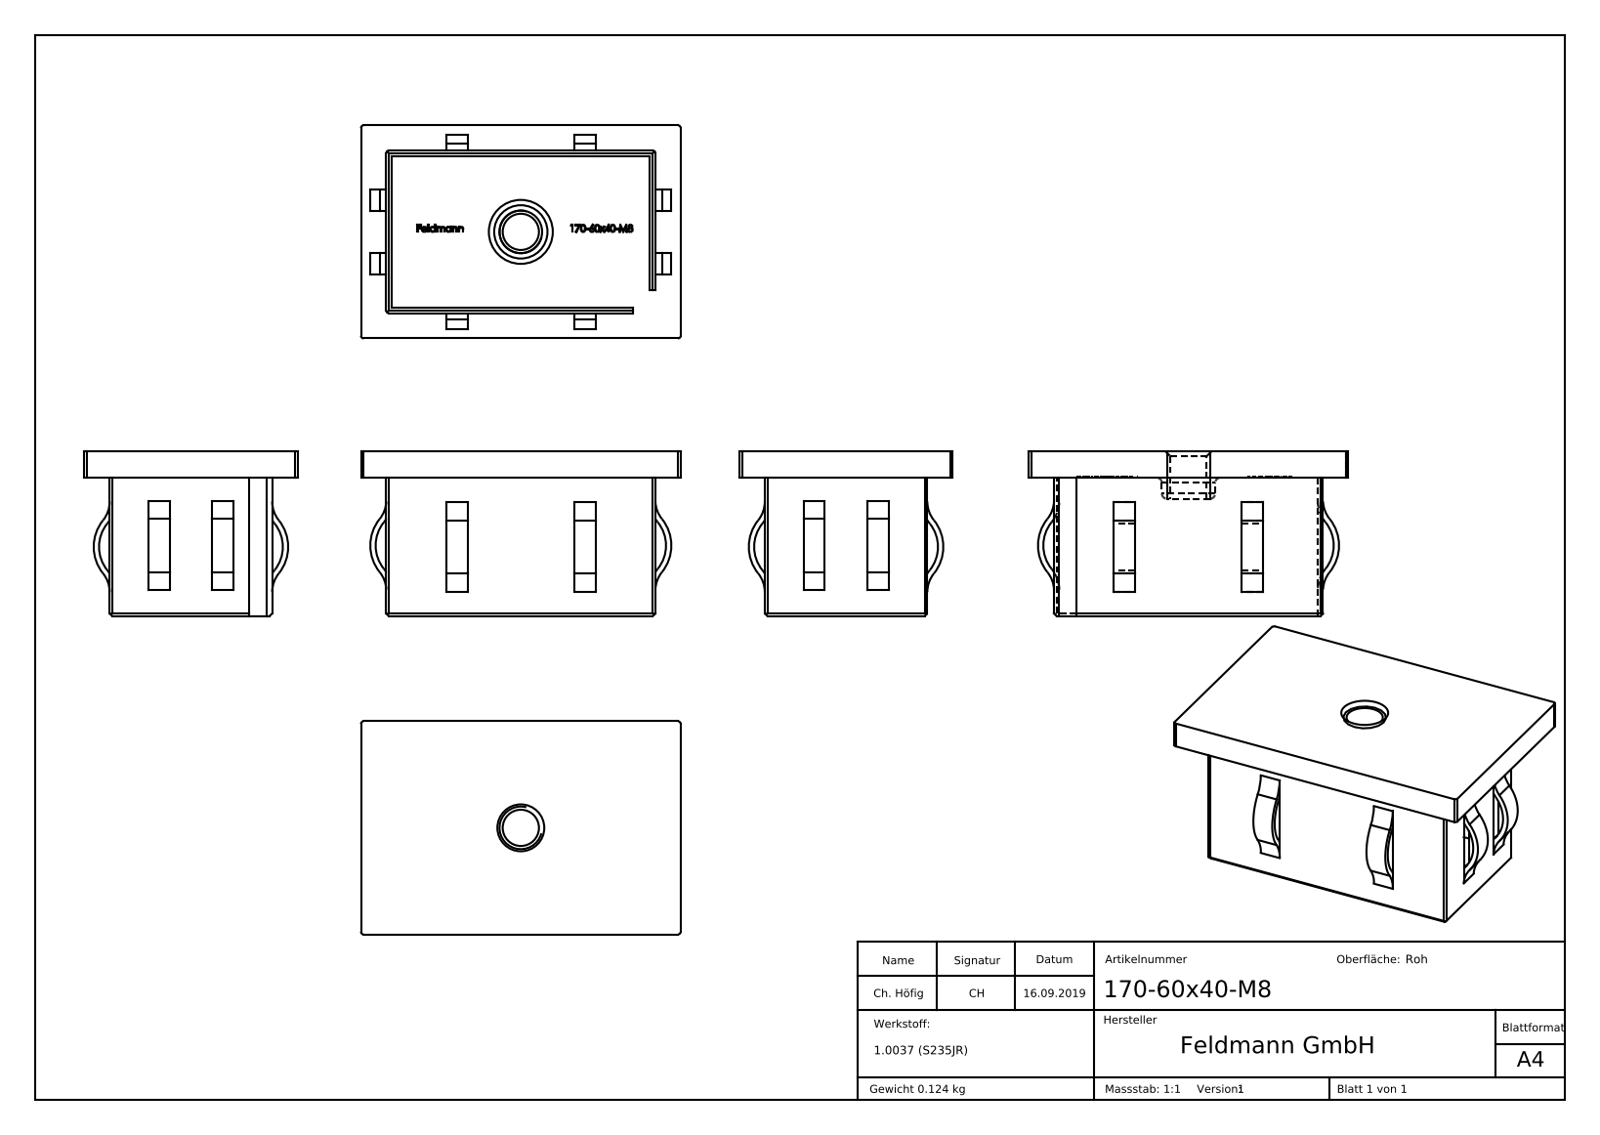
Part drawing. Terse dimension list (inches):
name: 170-60x40-M8
written by: SolidWorks 2015 (CONFIG_CONTROL_DESIGN)
unit: in
bodies: 1 solid, 377 faces (190 planar, 67 cylindrical, 120 other)
size: 2.362 × 1.575 × 1.22
volume: 0.971 in³; area: 22.21 in²
holes: 1× ⌀0.268
bosses: 1× ⌀0.394
rounds: 8× R0.22, 7× R0.02, 4× R0.259, 4× R0.259, 2× R0.274, 2× R0.274, 2× R0.313, 2× R0.314
face distances: 0.039, 0.197, 1.161, 1.949, 1.122, 1.201, 0.187, 0.226, 1.348, 1.388
